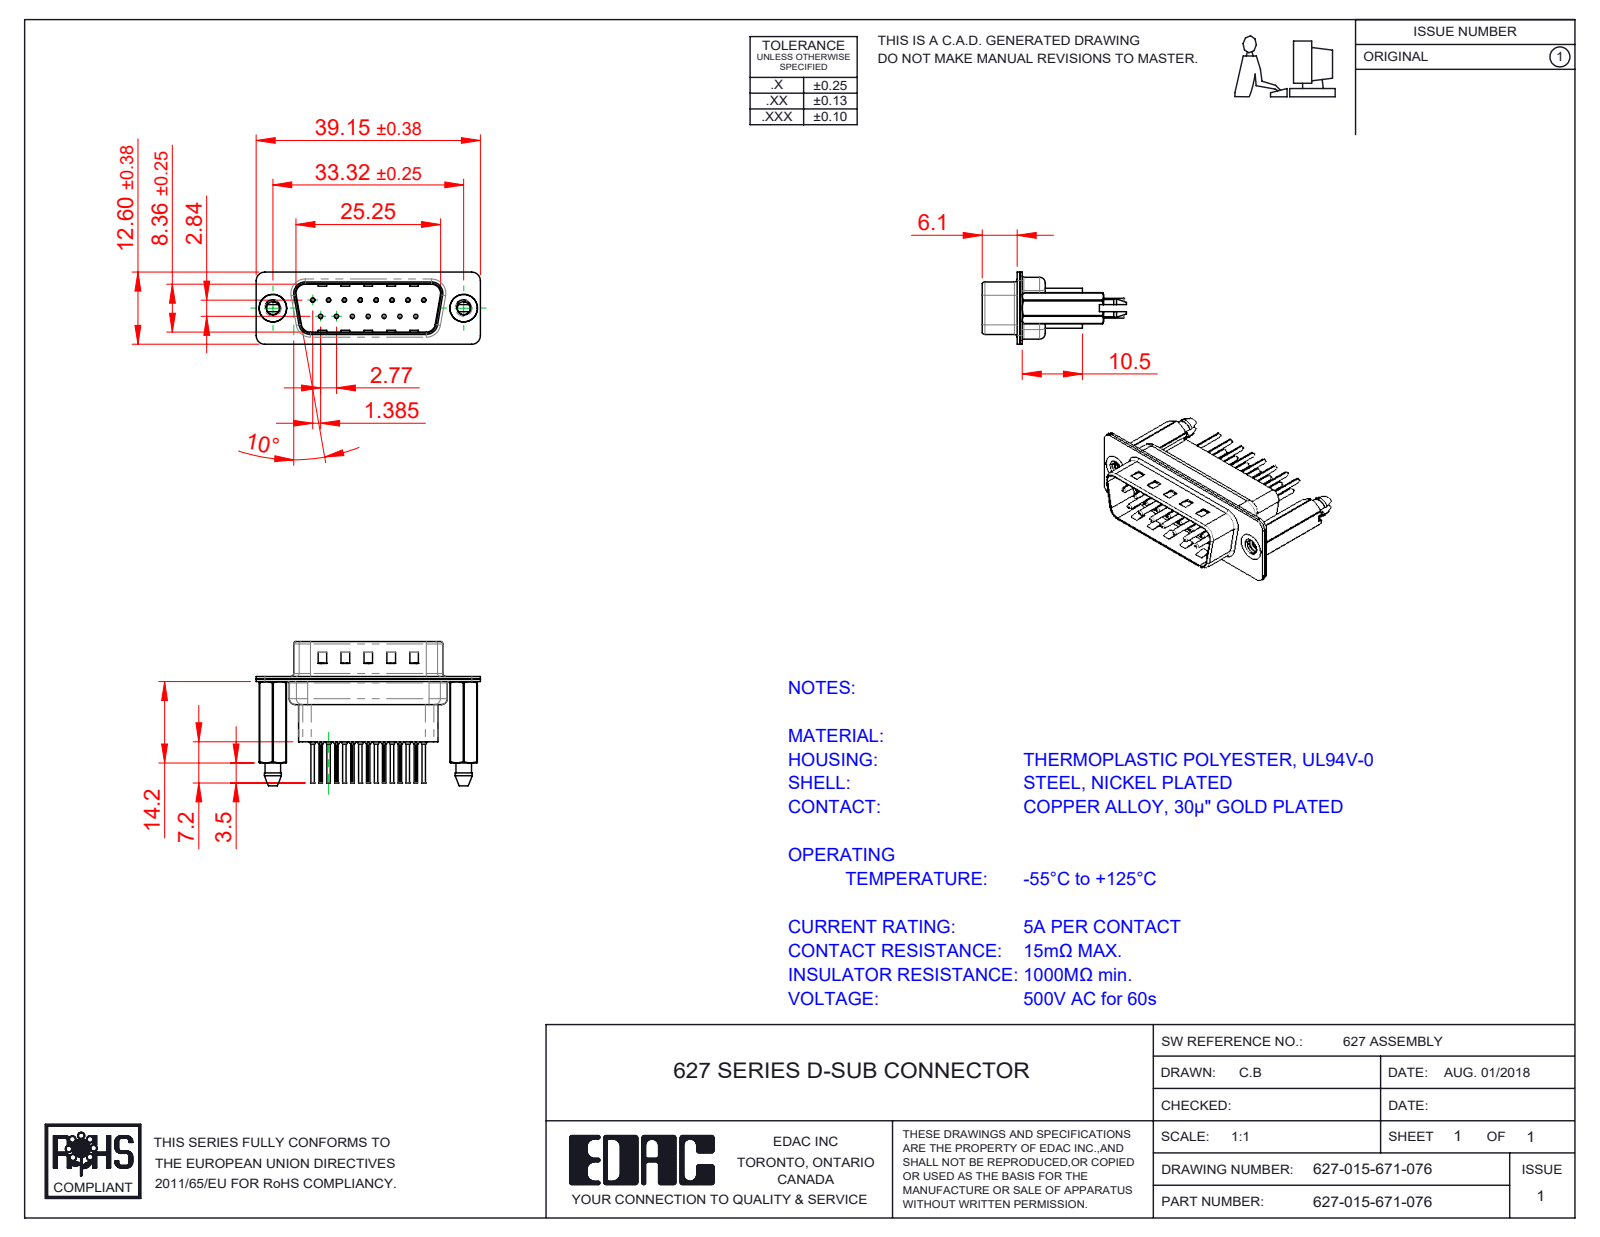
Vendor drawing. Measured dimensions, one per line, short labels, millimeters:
name: 627 4-40 Threaded Boardlock_HP71; 627 Contact Row 1_61; 627 Shell Front_15 Contacts; 627-015-671-076 (+3 more)
written by: SolidWorks 2020 (CONFIG_CONTROL_DESIGN)
unit: mm
bodies: 20 solids, 1918 faces (531 planar, 754 cylindrical, 633 other)
size: 39.15 × 25.1 × 12.6
volume: 2 911 mm³; area: 7 517 mm²
holes: 15× ⌀0.2, 15× ⌀0.35, 15× ⌀1.1, 15× ⌀1.6, 2× ⌀2.26, 2× ⌀4, 2× ⌀4.8
bosses: 15× ⌀2, 15× ⌀1.5, 15× ⌀0.75, 15× ⌀0.6, 2× ⌀4.9
rounds: 30× R0.1, 18× R1.5, 12× R2, 10× R1.6, 8× R0.5, 4× R0.25, 4× R0.6, 4× R0.65
face distances: 0.4, 0.45, 0.9, 0.82, 9.58, 4.76, 1.5, 0.68, 7.68, 1.4
hole spacings: 3.16, 2.77, 5.54, 8.31, 11.08, 5.03, 5.04, 7.48
